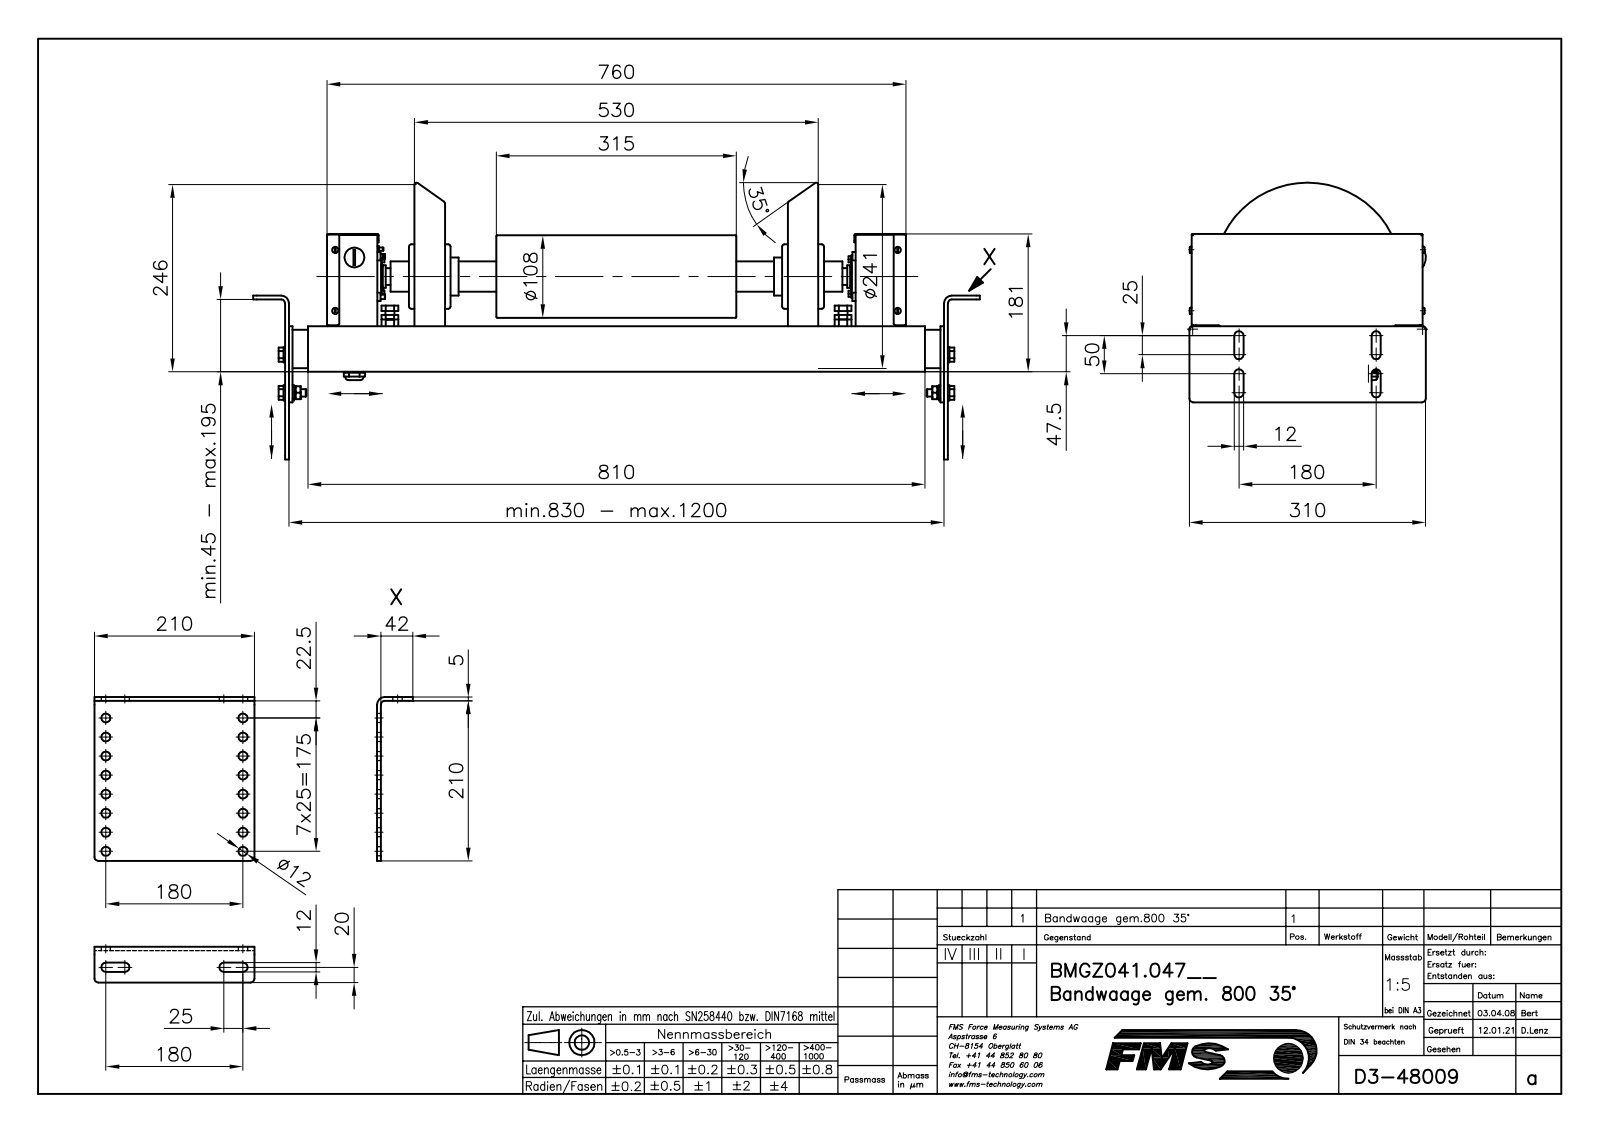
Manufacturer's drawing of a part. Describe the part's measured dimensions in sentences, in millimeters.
The part is named "B48009_STP; B50030; 6KT-SCHRAUBE_M12X30; ZYL_SCHR__M4X8 (+8 more)". Its 3-D file was written by "Mechanical Desktop 2009 (CONFIG_CONTROL_DESIGN)". It is 156 solids with 2658 faces: 1351 planar, 944 cylindrical and 363 other. Overall it measures 954 by 363.21 by 310.2 millimeters. Its volume is 8 272 000 cubic millimeters and its surface area 2 698 000 square millimeters. Round holes: 17 of diameter 12, 6 of diameter 5, 4 of diameter 3.5, 4 of diameter 4.9, 4 of diameter 6.4, 4 of diameter 8.68, 4 of diameter 8.75, 4 of diameter 10, 4 of diameter 10.5, 4 of diameter 10.68, 4 of diameter 14.8, 3 of diameter 6. Round bosses or shafts: 11 of diameter 12, 8 of diameter 8.2, 8 of diameter 4.2, 6 of diameter 20, 6 of diameter 10, 5 of diameter 5, 4 of diameter 16, 4 of diameter 11.1. Partial cylindrical surfaces (rounded edges, fillets, slot ends): 34 of radius 2, 24 of radius 1, 16 of radius 4, 16 of radius 5, 14 of radius 6, 8 of radius 3.5, 6 of radius 2.25, 4 of radius 0.5. The main face-to-face distances are 4, 5, 1, 51, 56, 36, 270, 50, 3, 55. The hole center spacings are 25, 181.73, 50, 75, 186.82, 195, 100, 180.
